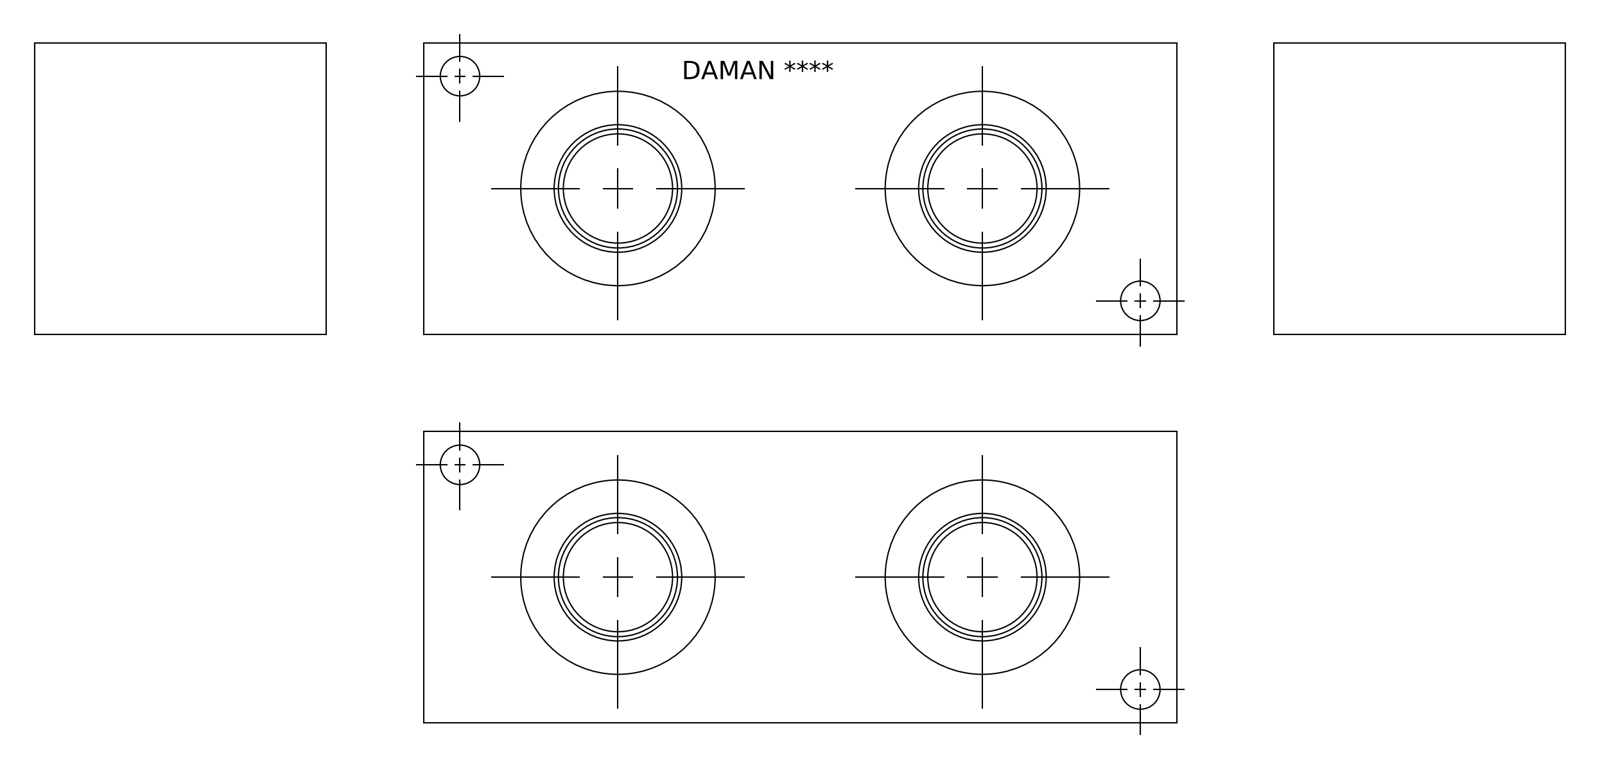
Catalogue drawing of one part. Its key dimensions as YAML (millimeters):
part_name: "Part_+J0900216S_3D"
step_written_by: "Autodesk Inventor 2020 (AUTOMOTIVE_DESIGN)"
units: millimeters
bodies: {solids: 1, faces: 385, planar: 213, cylindrical: 31, other: 141}
overall_size: [196.85, 76.2, 76.2]
volume: 1005000
surface_area: 91871
round_holes:
  - {diameter: 10.31, count: 4}
  - {diameter: 28.57, count: 4}
  - {diameter: 31.27, count: 4}
  - {diameter: 33.76, count: 4}
  - {diameter: 49.12, count: 4}
  - {diameter: 33.35, count: 3}
  - {diameter: 35.51, count: 3}
  - {diameter: 33.34, count: 1}
face_to_face_distances: [76.2, 196.85, 0.79, 75.41, 19.84, 19.05, 56.36, 76.16, 19.8, 0.75]
hole_center_spacings: [50.65, 139.64, 95.25, 187.24]
